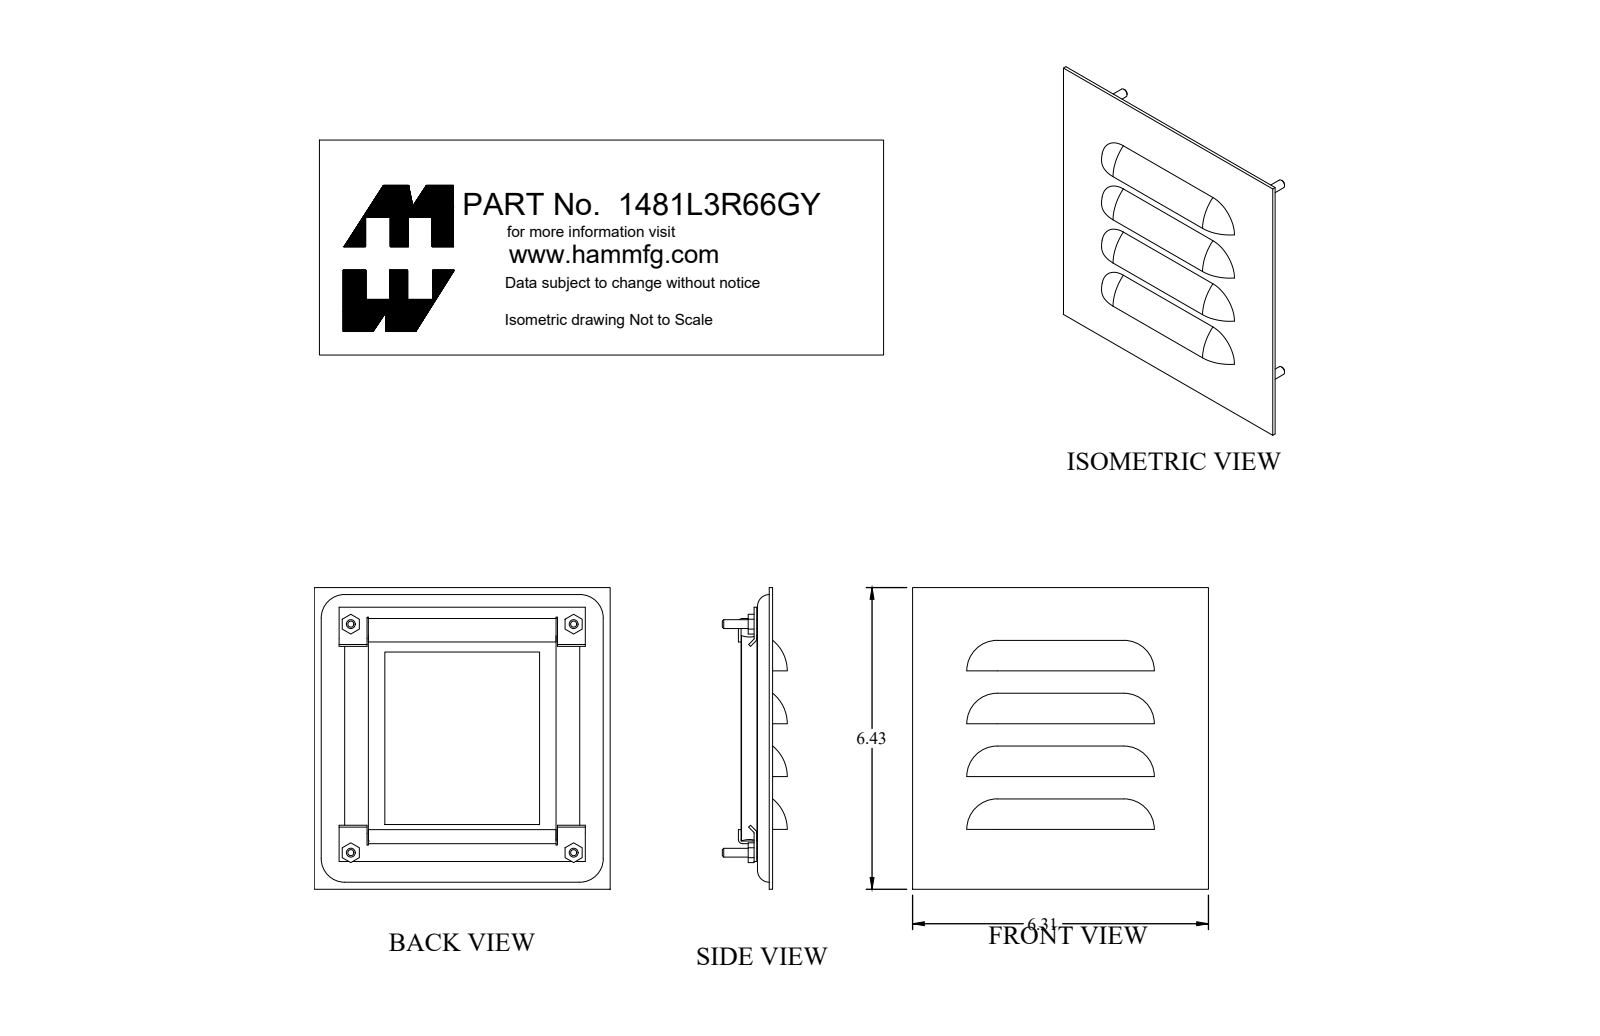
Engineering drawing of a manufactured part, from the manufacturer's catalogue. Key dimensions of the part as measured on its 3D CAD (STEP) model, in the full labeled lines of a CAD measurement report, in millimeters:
Part name (STEP PRODUCT): 1481L3R66GY_Default
STEP written by: SolidWorks 2019 (CONFIG_CONTROL_DESIGN)
Units: millimetres
Bodies: 13 solids, 248 faces (140 planar, 72 cylindrical, 36 other)
Overall size (bounding box): 163.3 × 160.2 × 35.2
Volume: 175 200 mm³ · Surface area: 133 400 mm²
Round holes (diameter × count): ⌀4 ×4, ⌀5.2 ×4
Round bosses / shafts (diameter × count): ⌀6.4 ×4, ⌀4.8 ×4
Partial cylindrical surfaces — rounded edges, fillets, slot ends (radius × count): R0.7 ×6, R2.2 ×6, R6.4 ×4, R11.9 ×4, R12.7 ×4, R19.3 ×4, R21.2 ×4
Main face-to-face distances: 1.8, 7.6, 6.4, 1.3, 9.4, 15.8, 14, 1.9, 7.6, 13.9
Hole centre spacings: 123.7, 120.7, 120.7, 172.8, 172.8
